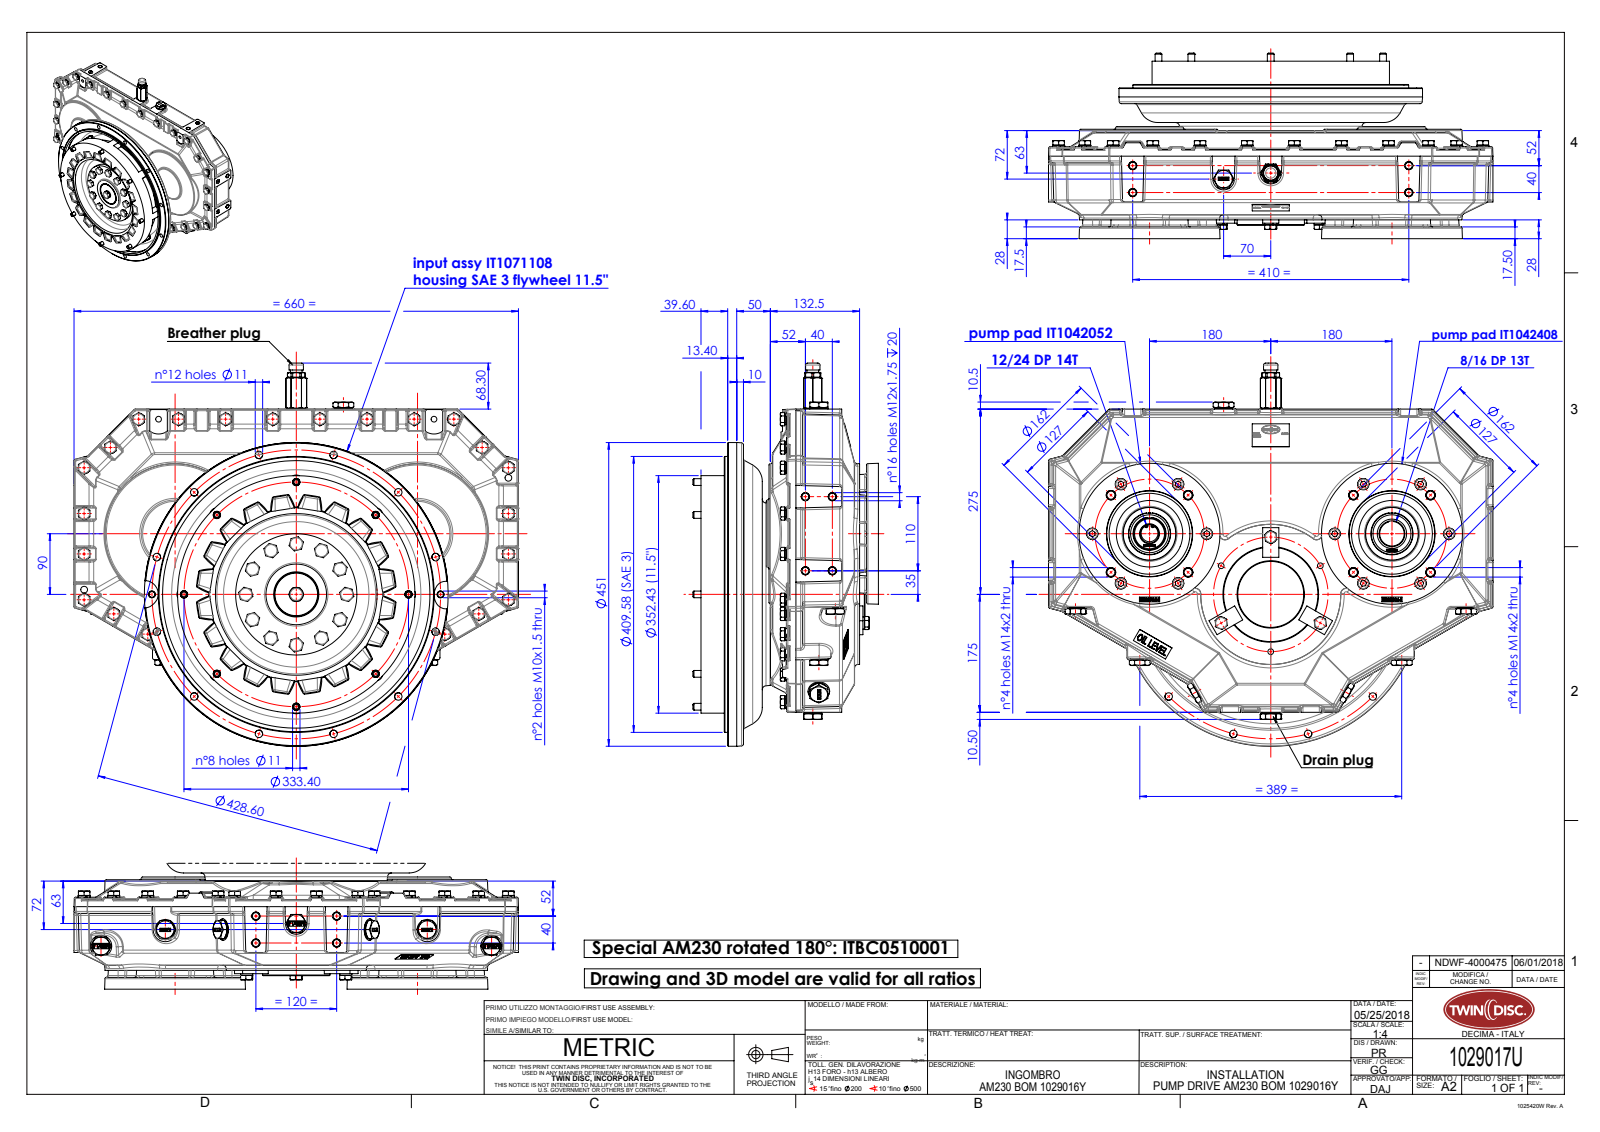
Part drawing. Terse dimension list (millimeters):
name: ITam230-001_rev01-installation; IT1042052_rev00-installation; ITBC0510000-installation; IT0000198_rev00-installation (+7 more)
written by: SolidWorks 2015 (AUTOMOTIVE_DESIGN)
unit: mm
bodies: 47 solids, 8432 faces (3692 planar, 2170 cylindrical, 2570 other)
size: 660 × 568.8 × 275.5
volume: 9 161 000 mm³; area: 3 018 000 mm²
holes: 52× ⌀10.2, 47× ⌀11, 38× ⌀10.5, 32× ⌀8.5, 21× ⌀12, 19× ⌀13, 12× ⌀10, 12× ⌀17, 8× ⌀14, 7× ⌀12.2, 5× ⌀21, 4× ⌀18.63
bosses: 53× ⌀10, 41× ⌀16.2, 33× ⌀18.1, 19× ⌀18, 19× ⌀12, 12× ⌀24, 12× ⌀16, 8× ⌀21
rounds: 199× R2, 158× R2.5, 127× R3, 78× R1.5, 74× R5, 58× R0.45, 18× R13, 12× R10.97
face distances: 20, 28, 48, 30, 132.5, 40, 15, 18, 5, 19
hole spacings: 57.4, 120, 138.58, 40, 207.84, 22.59, 51.37, 66.61
